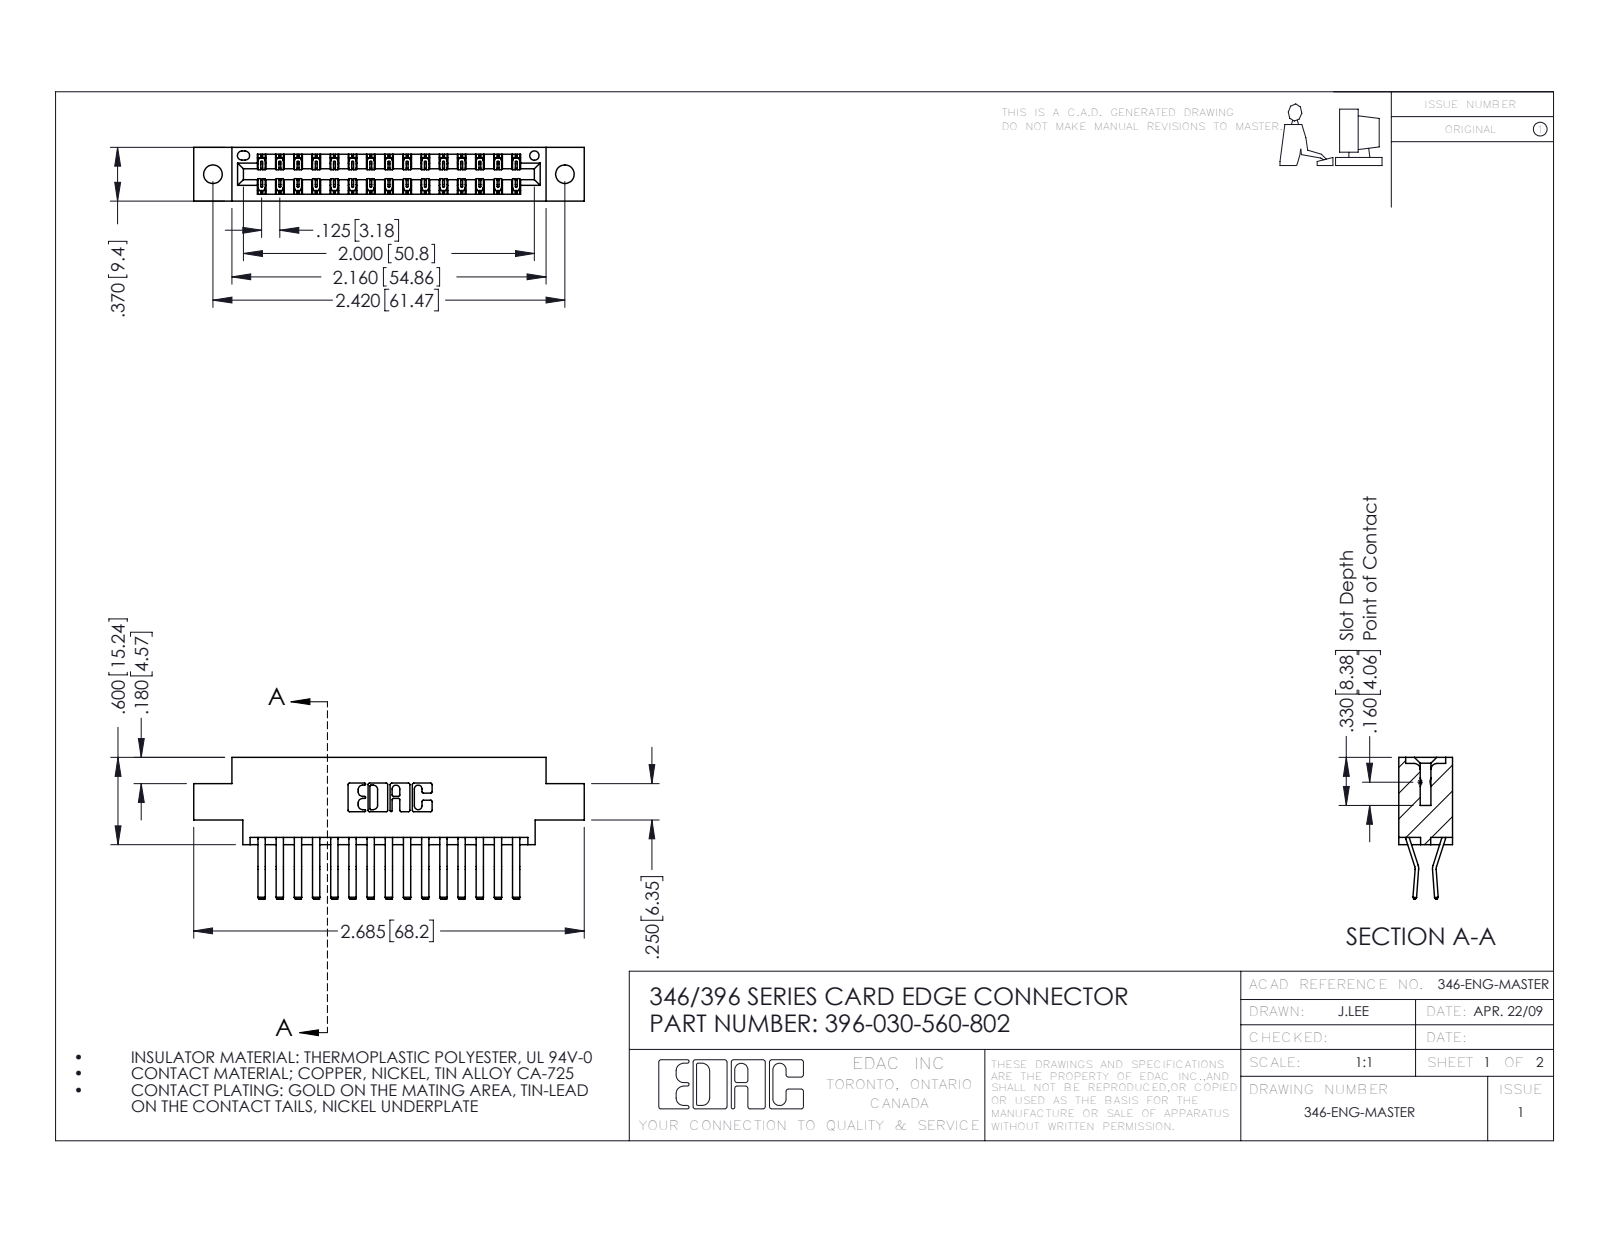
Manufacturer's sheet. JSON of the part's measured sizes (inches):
{"part_name": "396-030-560-802; 345-292-001_560 Tail; 346 Part_0.170 Offset - 0.128 Dia", "step_written_by": "SolidWorks 2016 (CONFIG_CONTROL_DESIGN)", "units": "inches", "bodies": {"solids": 31, "faces": 1746, "planar": 1130, "cylindrical": 616, "other": 0}, "overall_size": [2.685, 0.975, 0.37], "volume_in3": 0.393, "surface_area_in2": 13.75, "round_holes": [[0.128, 2], [0.064, 1]], "partial_cylinders_radius": [[0.006, 45], [0.01, 22], [0.007, 6], [0.031, 6], [0.026, 3], [0.01, 2], [0.014, 2], [0.022, 2]], "face_to_face_distances": [0.048, 0.322, 0.37, 0.25, 0.025, 0.072, 0.298, 0.275, 0.148, 0.222], "hole_center_spacings": [0.246, 2.213, 2.42]}
